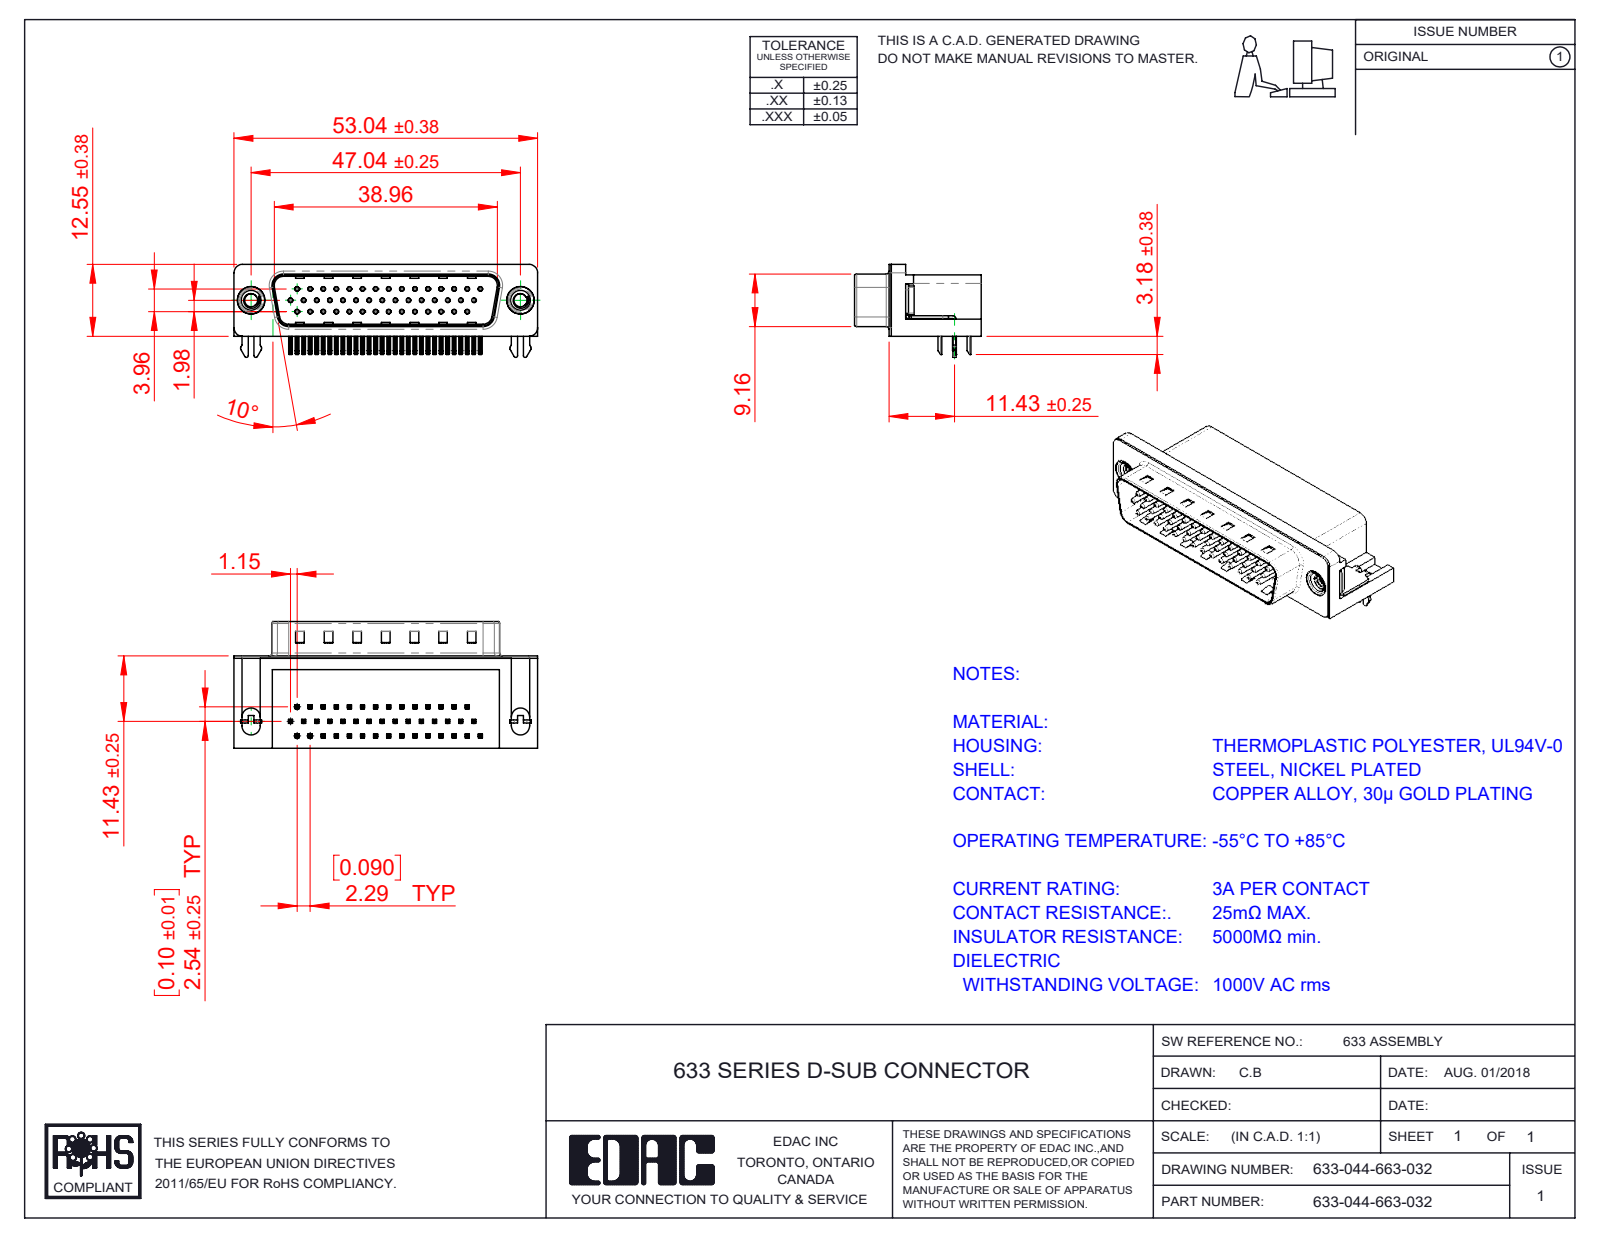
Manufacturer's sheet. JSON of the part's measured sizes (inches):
{"part_name": "633 Housing_44 Contact; 633 Contact Middle; 633 Contact Bottom; 633 4-40 Threaded Rivet (+4 more)", "step_written_by": "SolidWorks 2016 (CONFIG_CONTROL_DESIGN)", "units": "inches", "bodies": {"solids": 50, "faces": 3730, "planar": 2349, "cylindrical": 1068, "other": 313}, "overall_size": [2.088, 0.87, 0.64], "volume_in3": 0.495, "surface_area_in2": 15.85, "round_holes": [[0.014, 44], [0.031, 44], [0.089, 2], [0.157, 2], [0.189, 2], [0.197, 2]], "round_bosses_or_shafts": [[0.03, 44], [0.193, 2], [0.187, 2], [0.154, 2]], "partial_cylinders_radius": [[0.01, 184], [0.005, 88], [0.039, 16], [0.02, 14], [0.063, 8], [0.059, 7], [0.013, 4], [0.035, 4]], "face_to_face_distances": [0.016, 0.407, 0.618, 0.345, 0.114, 0.098, 0.083, 0.634, 0.421, 0.1], "hole_center_spacings": [0.09, 0.18, 0.18, 0.09, 0.27, 0.361, 0.451, 0.089]}
